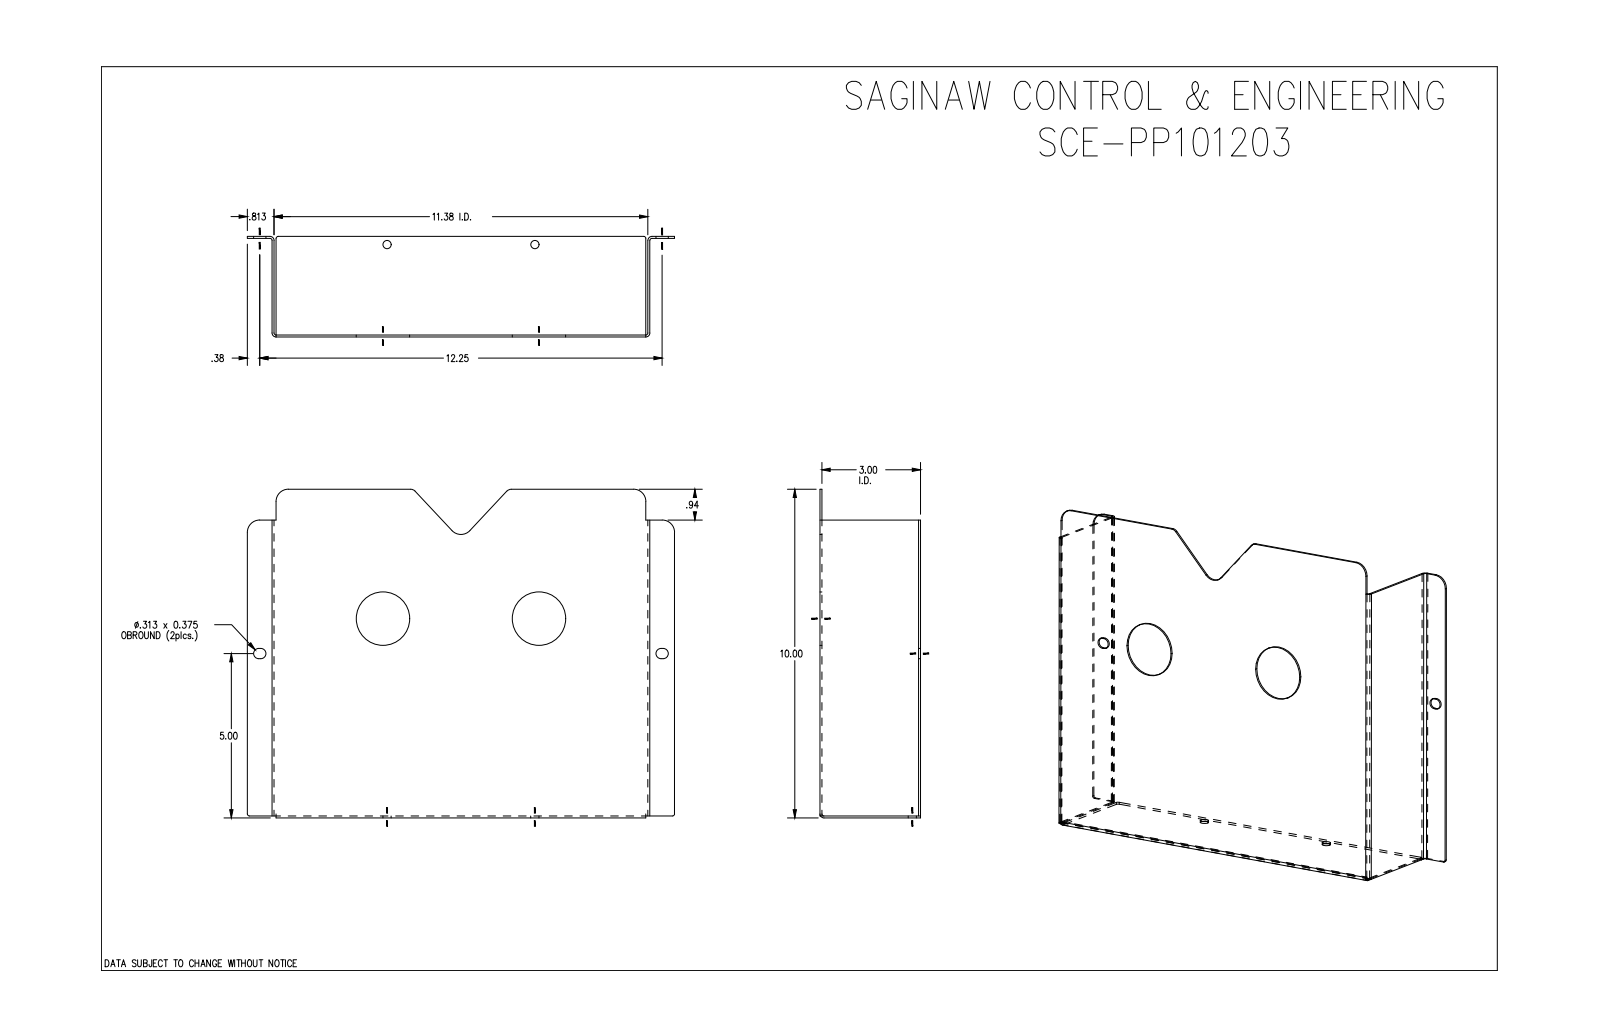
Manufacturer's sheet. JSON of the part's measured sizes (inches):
{"part_name": "SCE-PP101203", "step_written_by": "SolidWorks 2019 (CONFIG_CONTROL_DESIGN)", "units": "inches", "bodies": {"solids": 1, "faces": 84, "planar": 49, "cylindrical": 33, "other": 2}, "overall_size": [13.005, 10, 3.06], "volume_in3": 12.44, "surface_area_in2": 419.5, "round_holes": [[0.25, 2], [1.625, 2]], "partial_cylinders_radius": [[0.062, 5], [0.375, 5], [0.156, 4], [0.122, 3], [0.063, 2], [0.065, 2], [0.125, 2], [0.188, 2]], "face_to_face_distances": [0.06, 11.5, 0.06, 11.44, 11.38, 11.44, 3, 3.06, 2.94, 0.813], "hole_center_spacings": [4.5, 4.75]}
